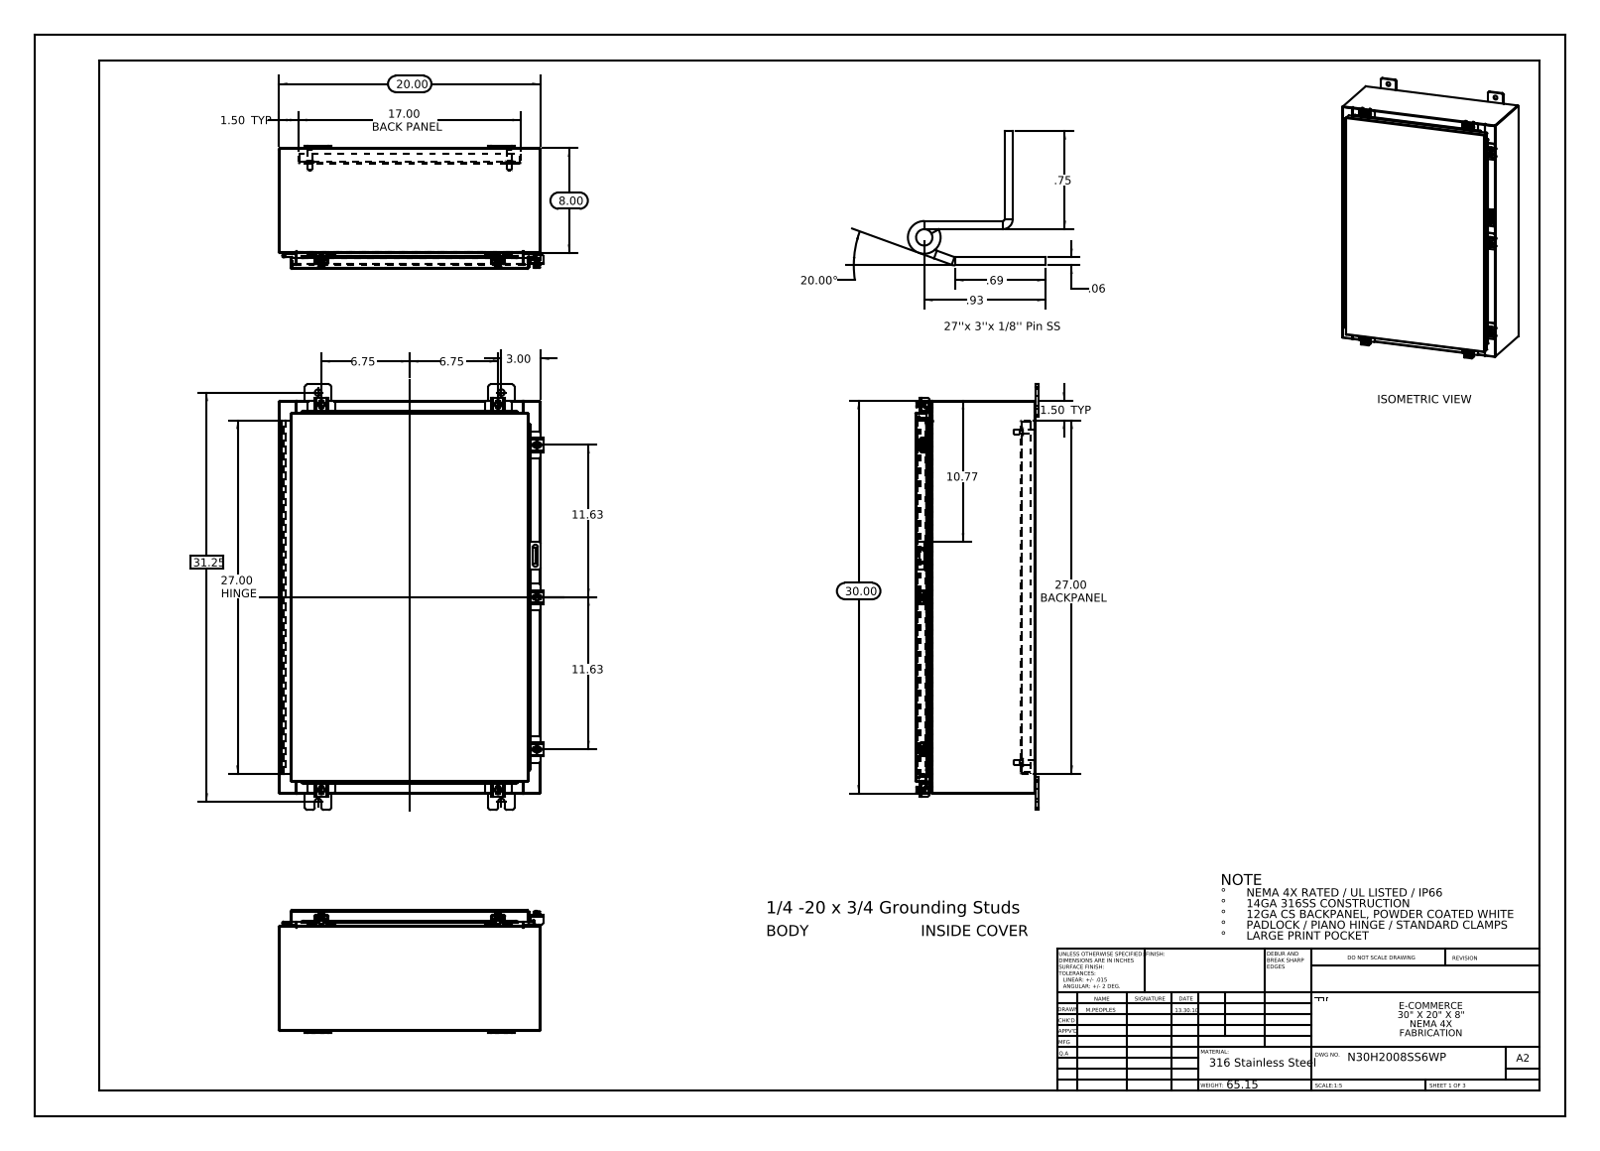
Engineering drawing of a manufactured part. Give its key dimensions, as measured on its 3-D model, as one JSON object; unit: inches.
{"part_name": "N30H2008SS6WP Body; N30H2008SS6WP Padlock Hasp; N30H2008SS6WP Mounting Studs; N30H2008SS6WP Mounting Feet (+8 more)", "step_written_by": "SolidWorks 2013 (CONFIG_CONTROL_DESIGN)", "units": "inches", "bodies": {"solids": 52, "faces": 1990, "planar": 1056, "cylindrical": 830, "other": 104}, "overall_size": [32.5, 20.211, 9.389], "volume_in3": 229, "surface_area_in2": 5746, "round_holes": [[0.5, 8], [0.213, 7], [0.26, 7], [0.125, 2], [0.125, 1]], "round_bosses_or_shafts": [[0.25, 8], [0.5, 7], [0.399, 7], [0.625, 4], [0.375, 4], [0.33, 4]], "partial_cylinders_radius": [[0.06, 34], [0.013, 27], [0.19, 24], [0.088, 21], [0.12, 14], [0.141, 14], [0.05, 11], [0.08, 10]], "face_to_face_distances": [0.075, 9.126, 9.201, 9.051, 0.104, 19.925, 1, 1.075, 8.051, 8.126], "hole_center_spacings": [27.365, 30.898, 0.431, 0.934, 1.858, 2.275, 2.276, 2.327]}
